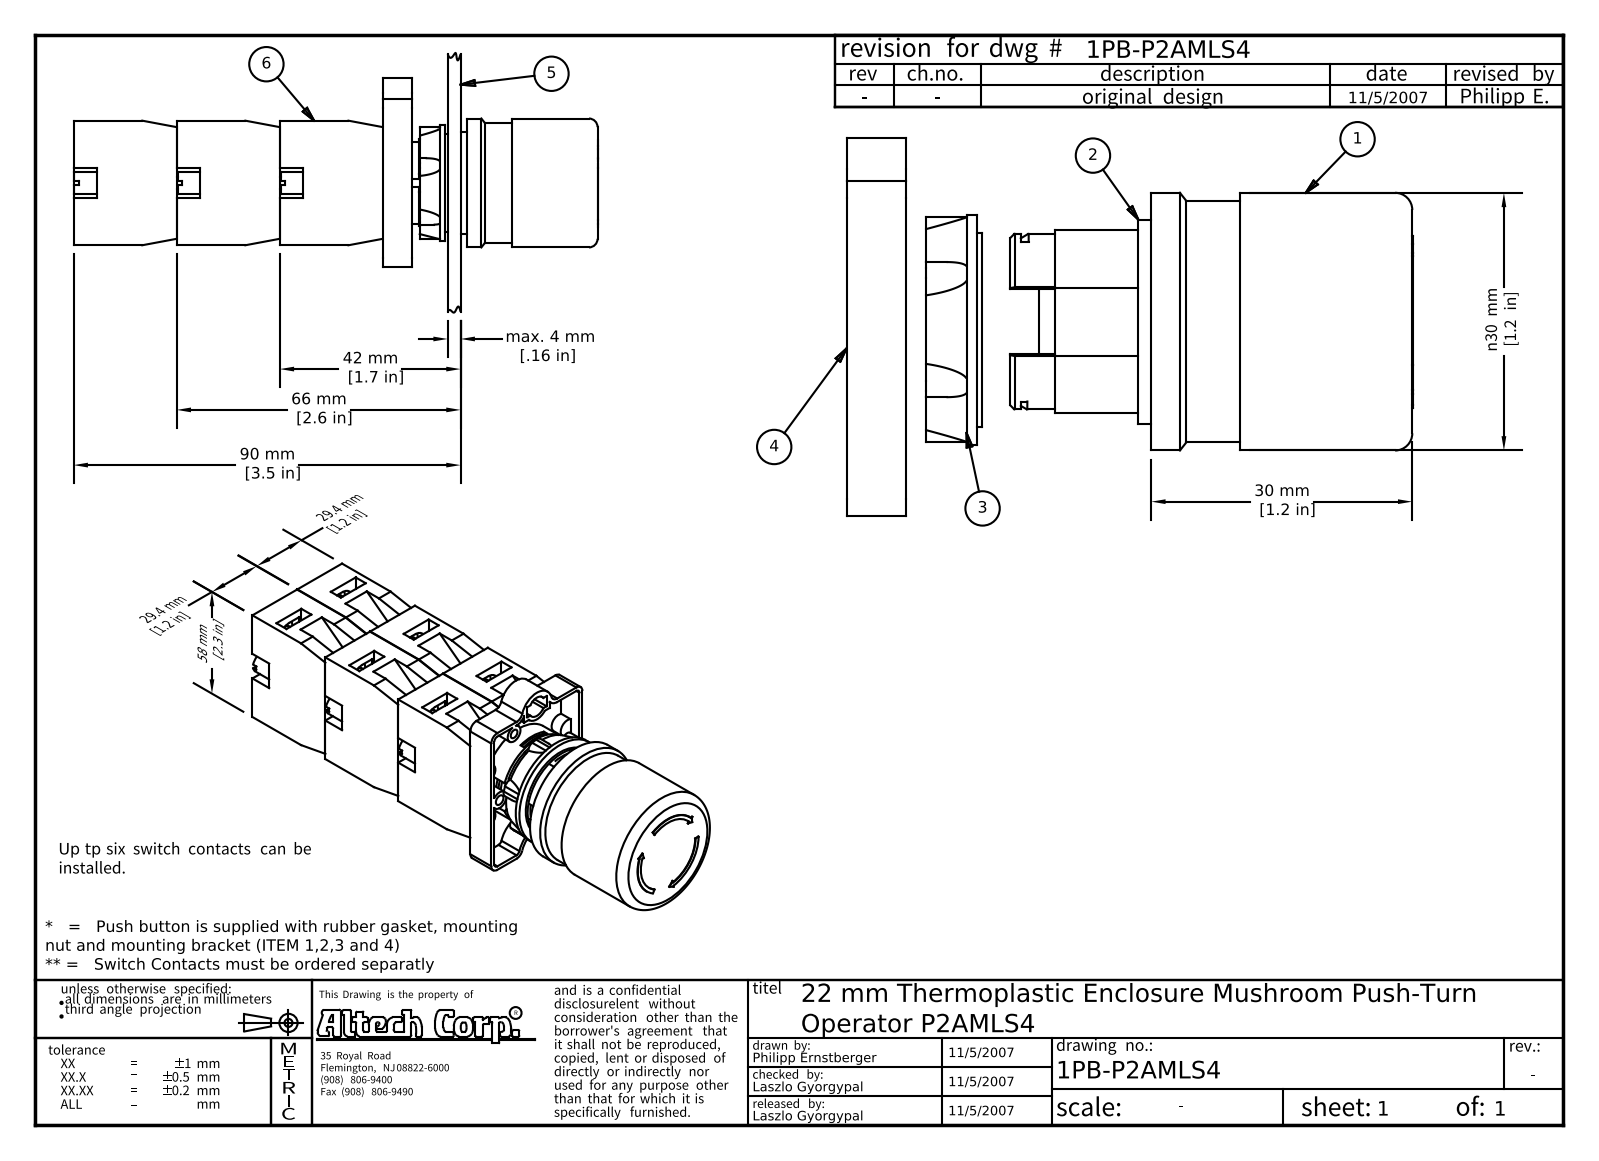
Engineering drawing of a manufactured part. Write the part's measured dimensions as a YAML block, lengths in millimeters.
part_name: "P2AMLS4_assembly; P2AMLS4_operator; P2AMLS4; 2PRG1 (+7 more)"
step_written_by: "Autodesk Inventor 2008 (AUTOMOTIVE_DESIGN)"
units: millimeters
bodies: {solids: 29, faces: 1182, planar: 647, cylindrical: 203, other: 332}
overall_size: [122.09, 60.45, 45]
volume: 87359
surface_area: 46371
round_holes:
  - {diameter: 2.5, count: 6}
  - {diameter: 2.2, count: 2}
  - {diameter: 2.6, count: 2}
  - {diameter: 17.6, count: 1}
  - {diameter: 20.8, count: 1}
  - {diameter: 22.5, count: 1}
  - {diameter: 28.3, count: 1}
round_bosses_or_shafts:
  - {diameter: 3, count: 6}
  - {diameter: 2.75, count: 4}
  - {diameter: 1.5, count: 4}
  - {diameter: 5, count: 2}
  - {diameter: 4.2, count: 2}
  - {diameter: 30, count: 1}
  - {diameter: 28.1, count: 1}
  - {diameter: 26.8, count: 1}
partial_cylinders:
  - {radius: 1, count: 15}
  - {radius: 1.5, count: 12}
  - {radius: 2, count: 8}
  - {radius: 2.25, count: 6}
  - {radius: 3, count: 2}
  - {radius: 3.3, count: 2}
  - {radius: 5, count: 2}
  - {radius: 2.6, count: 1}
face_to_face_distances: [14.8, 14.7, 24, 3, 48, 29.5, 29, 15.1, 18.1, 63.1]
hole_center_spacings: [6.54, 26.07, 11.41, 12.25, 13, 14.51, 14.56, 17.17]
